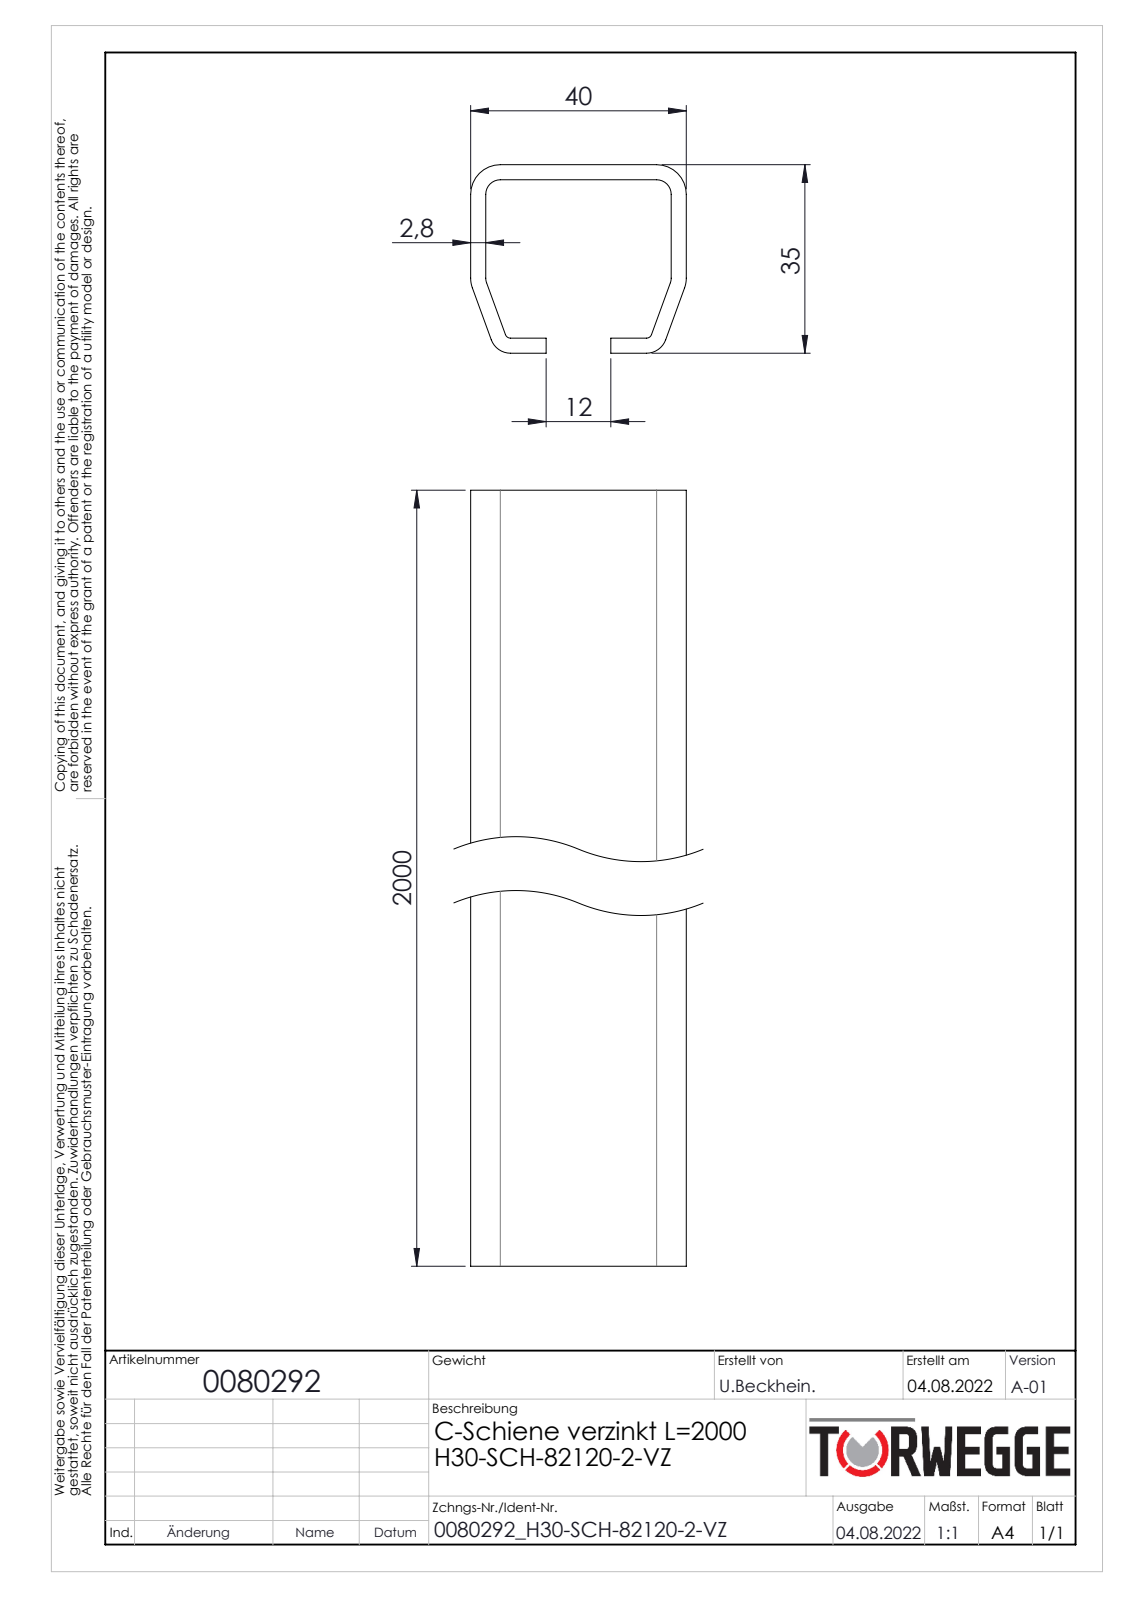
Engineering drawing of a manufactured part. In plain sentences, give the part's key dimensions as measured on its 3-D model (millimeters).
The part is named "0080292". Its 3-D file was written by "SolidWorks 2020 (AUTOMOTIVE_DESIGN)". It is 1 solid with 30 faces: 18 planar, 12 cylindrical and 0 other. Overall it measures 2000 by 40 by 35 millimeters. Its volume is 645 633 cubic millimeters and its surface area 473 012 square millimeters. Partial cylindrical surfaces (rounded edges, fillets, slot ends): 2 of radius 1, 2 of radius 2.5, 2 of radius 2.7, 2 of radius 3.8, 2 of radius 5.3, 2 of radius 5.5. The main face-to-face distances are 2.8, 37.2, 32.2, 40, 34.4, 35, 29.4, 14, 26, 11.2.
